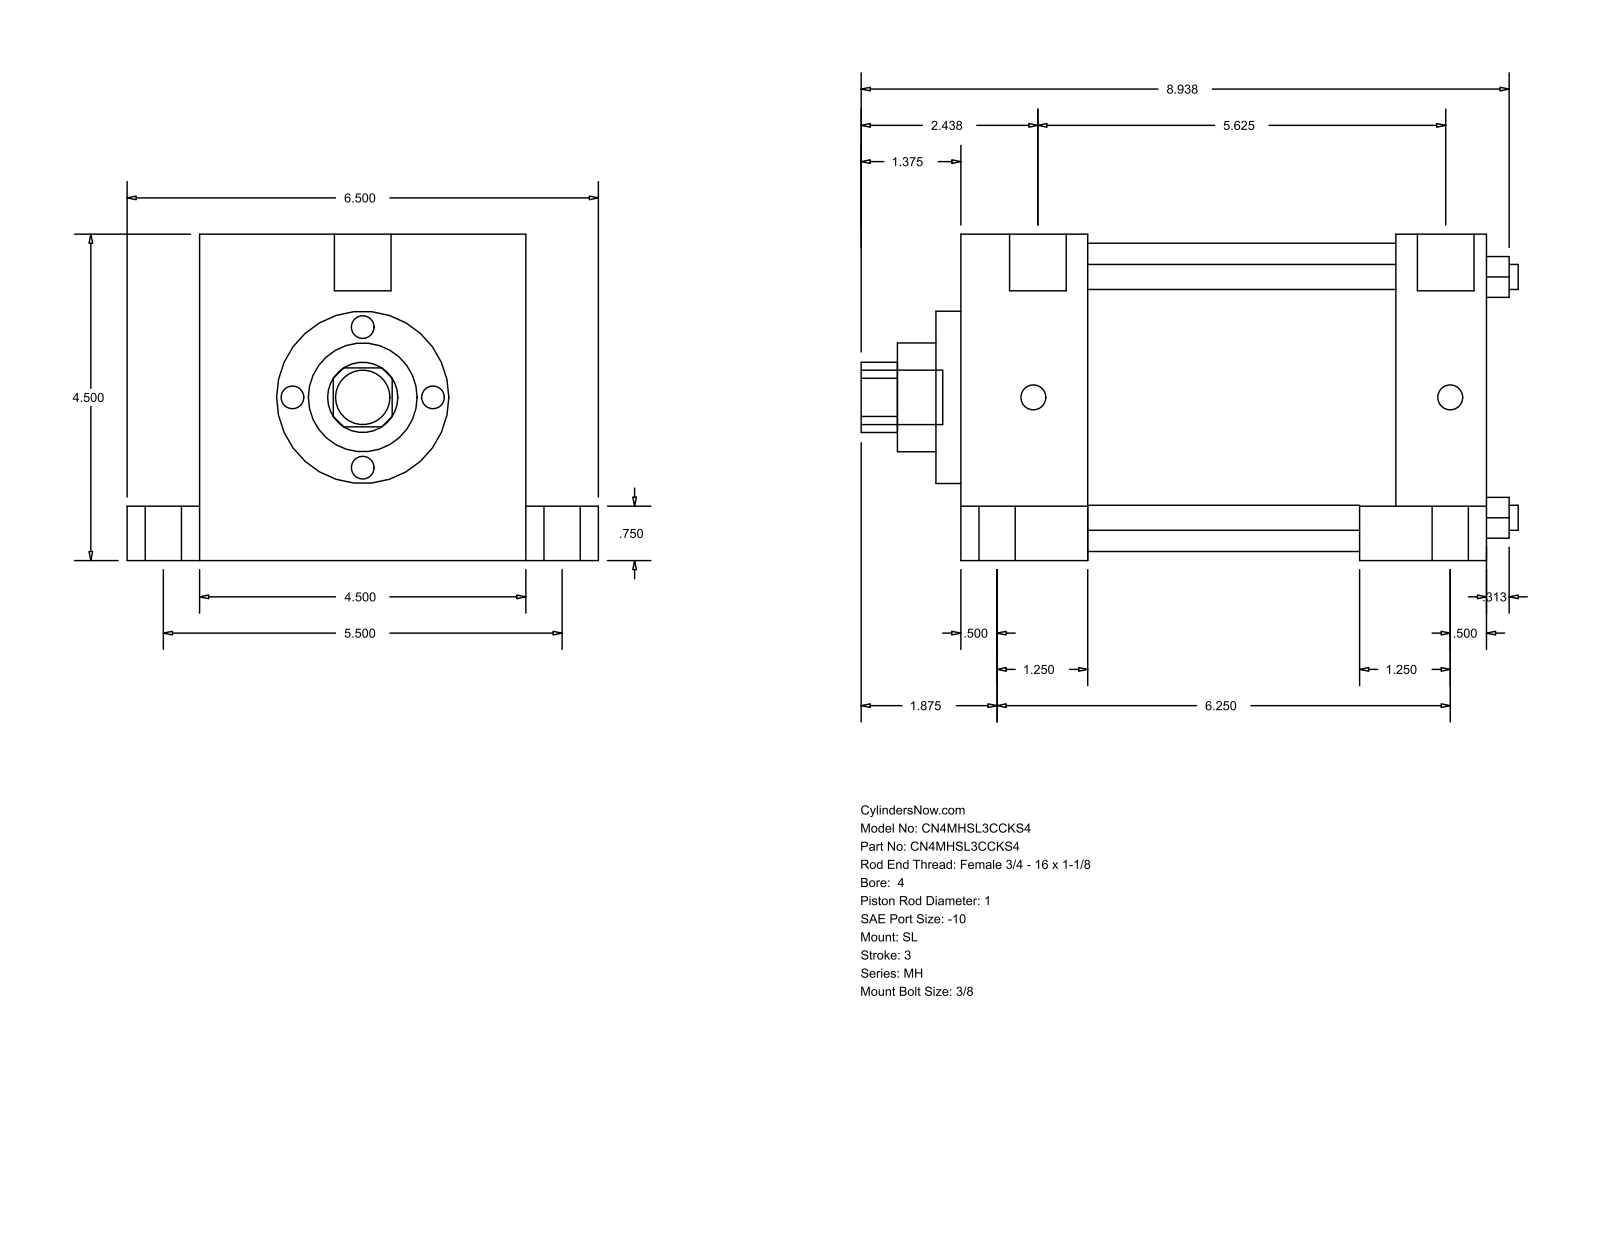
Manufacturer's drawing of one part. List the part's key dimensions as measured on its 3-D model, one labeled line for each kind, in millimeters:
Part name (STEP PRODUCT): MH_SL__0400_1
STEP written by: GSSL Pune (CONFIG_CONTROL_DESIGN)
Units: millimetres
Bodies: 0 solids, 110 faces (77 planar, 33 cylindrical, 0 other)
Overall size (bounding box): 230.19 × 165.1 × 114.3
Round holes (diameter × count): ⌀8.76 ×4, ⌀25.4 ×1, ⌀38.1 ×1, ⌀60.33 ×1, ⌀107.95 ×1
Round bosses / shafts (diameter × count): ⌀19.05 ×5, ⌀12.7 ×4, ⌀8.73 ×4, ⌀19.84 ×2
Partial cylindrical surfaces — rounded edges, fillets, slot ends (radius × count): R12.29 ×1
Main face-to-face distances: 114.3, 184.15, 44.46, 139.69, 139.7, 152.4, 107.94, 31.75, 25.4, 19.05
Hole centre spacings: 59.62, 84.32, 119.25
